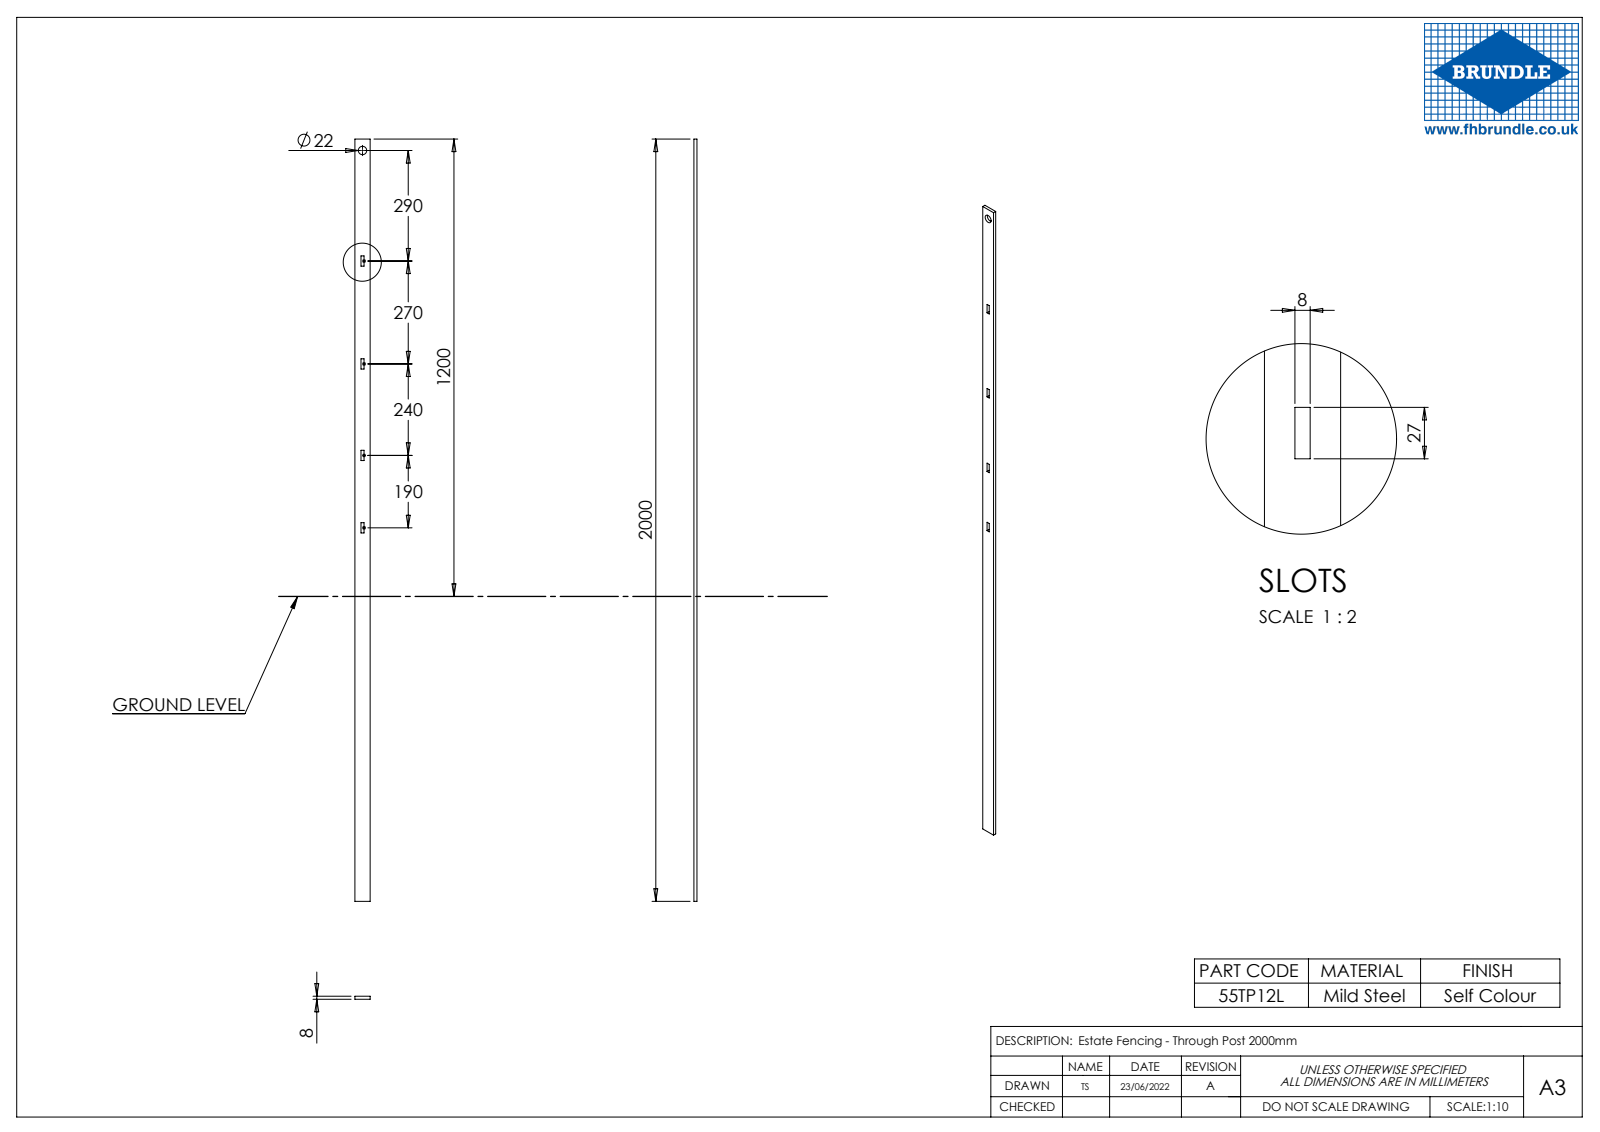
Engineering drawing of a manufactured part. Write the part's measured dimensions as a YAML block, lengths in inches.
part_name: "65TP12L"
step_written_by: "SolidWorks 2020 (CONFIG_CONTROL_DESIGN)"
units: inches
bodies: {solids: 1, faces: 24, planar: 22, cylindrical: 2, other: 0}
overall_size: [78.74, 1.575, 0.315]
volume: 38.45
surface_area: 299.1
round_holes:
  - {diameter: 0.866, count: 1}
face_to_face_distances: [0.315, 1.575, 0.63, 0.945, 78.74, 1.063, 7.48, 16.929, 27.559, 9.449]
